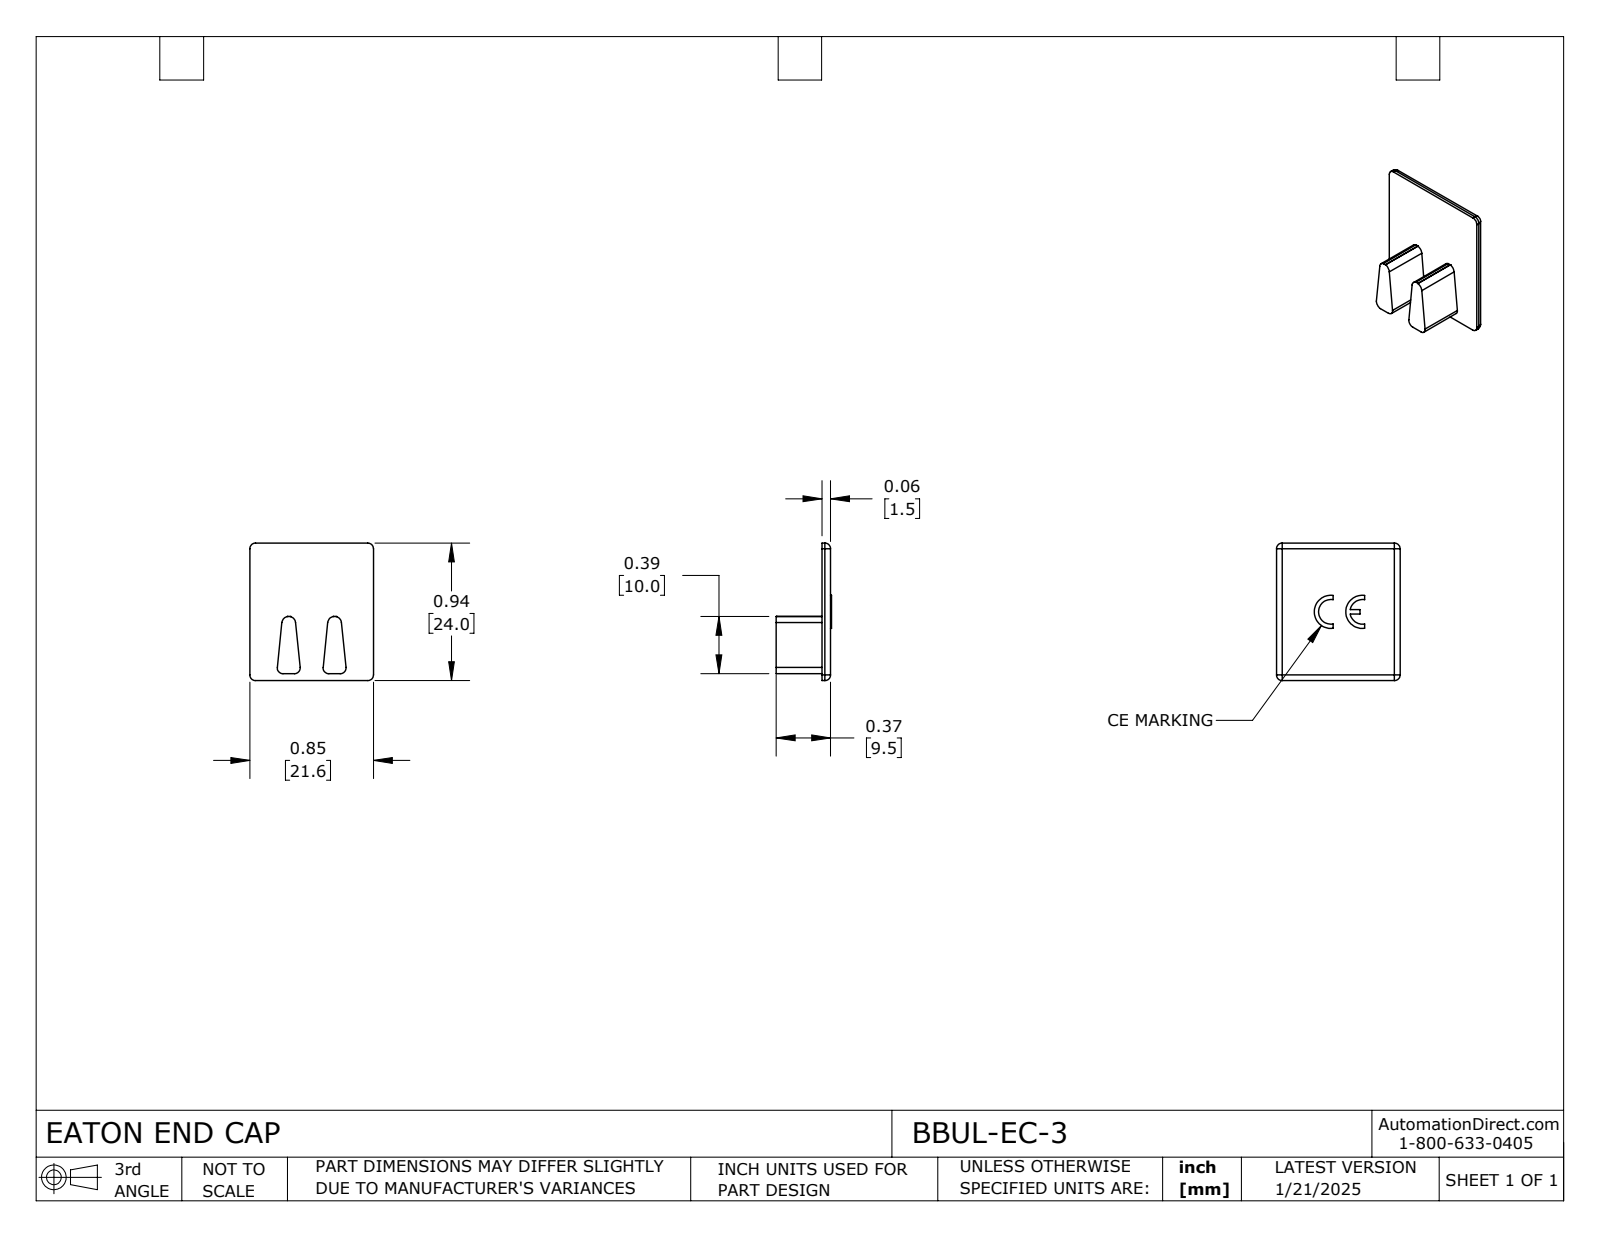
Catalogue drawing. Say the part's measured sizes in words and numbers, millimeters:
The part is named "BBUL-EC-3". Its 3-D file was written by "SolidWorks 2024 (CONFIG_CONTROL_DESIGN)". It is 1 solid with 56 faces: 29 planar, 23 cylindrical and 4 other. Overall it measures 24 by 21.6 by 9.65 millimeters. Its volume is 1 254 cubic millimeters and its surface area 1 531 square millimeters. Partial cylindrical surfaces (rounded edges, fillets, slot ends): 12 of radius 1, 2 of radius 1.2, 2 of radius 2.15, 2 of radius 2.9. The main face-to-face distances are 1.5, 7.96, 8, 9.5, 1.65, 9.65, 21.6, 1.2, 22.8, 24.
